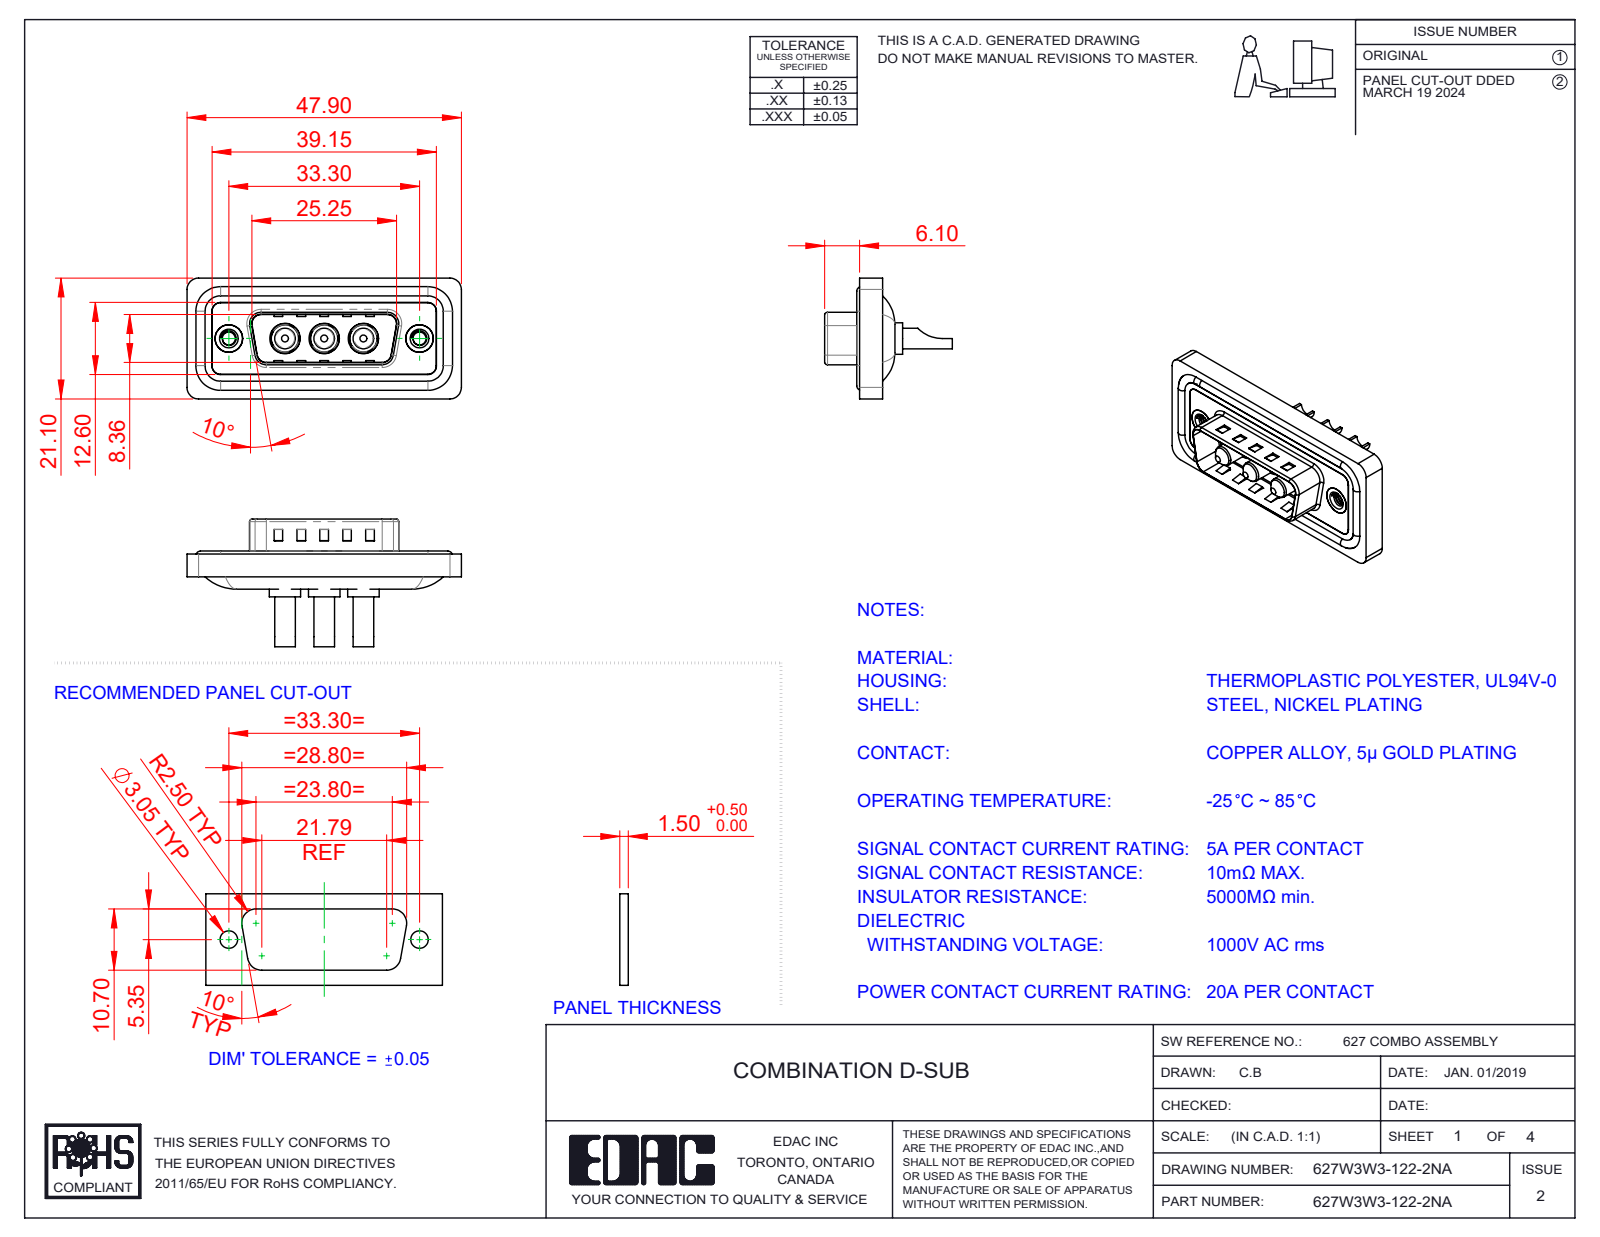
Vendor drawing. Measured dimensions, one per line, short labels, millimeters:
name: 627Combo Housing_3W3; 627Combo Threaded Rivet_A; Power Pin_20A SC; 627Combo Shell Front_15 Contacts (+3 more)
written by: SolidWorks 2023 (CONFIG_CONTROL_DESIGN)
unit: mm
bodies: 13 solids, 580 faces (216 planar, 252 cylindrical, 112 other)
size: 47.9 × 22.3 × 21.1
volume: 5 626 mm³; area: 8 998 mm²
holes: 3× ⌀2.7, 3× ⌀4.85, 3× ⌀5.3, 2× ⌀2.26, 2× ⌀4, 2× ⌀4.8, 2× ⌀5
bosses: 4× ⌀1.6, 3× ⌀5.5, 3× ⌀5.2, 3× ⌀4.75, 3× ⌀3.75, 3× ⌀3.6, 2× ⌀4.9
rounds: 26× R1.5, 20× R2, 8× R0.5, 8× R1.6, 4× R0.25, 4× R0.6, 4× R0.65, 4× R0.9
face distances: 0.4, 1.1, 1.5, 0.5, 1.6, 3.1, 2.9, 4, 0.82, 9.58
hole spacings: 6.85, 9.8, 16.65, 23.5, 13.7, 33.3
